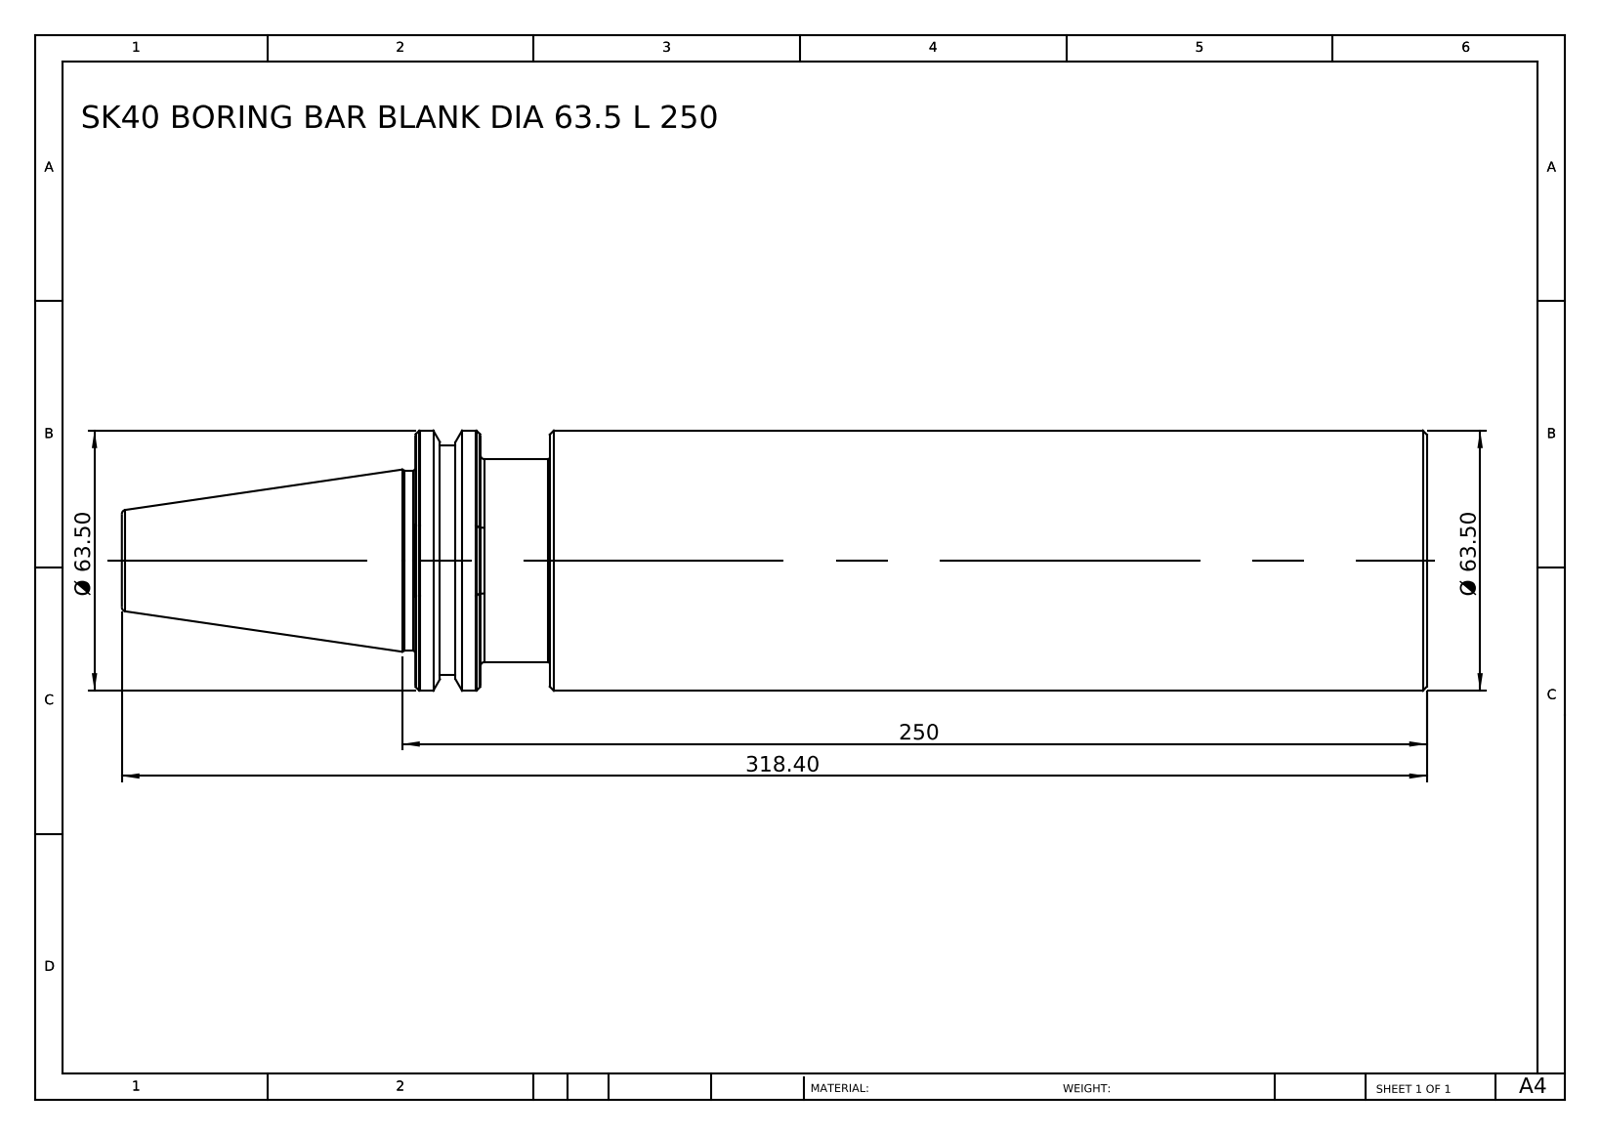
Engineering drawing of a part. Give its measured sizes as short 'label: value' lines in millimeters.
name: SK40 BORING BAR BLANK DIA 63.5 L 250
written by: SolidWorks 2014 (CONFIG_CONTROL_DESIGN)
unit: mm
bodies: 1 solid, 78 faces (7 planar, 12 cylindrical, 59 other)
size: 318.4 × 63.5 × 63.5
volume: 827 190 mm³; area: 64 402 mm²
bosses: 1× ⌀63.5, 1× ⌀56, 1× ⌀49.5, 1× ⌀44
face distances: 246.8, 214, 32.8, 230.9, 16.9, 15.9, 318.4, 104.4, 87.5, 71.6
